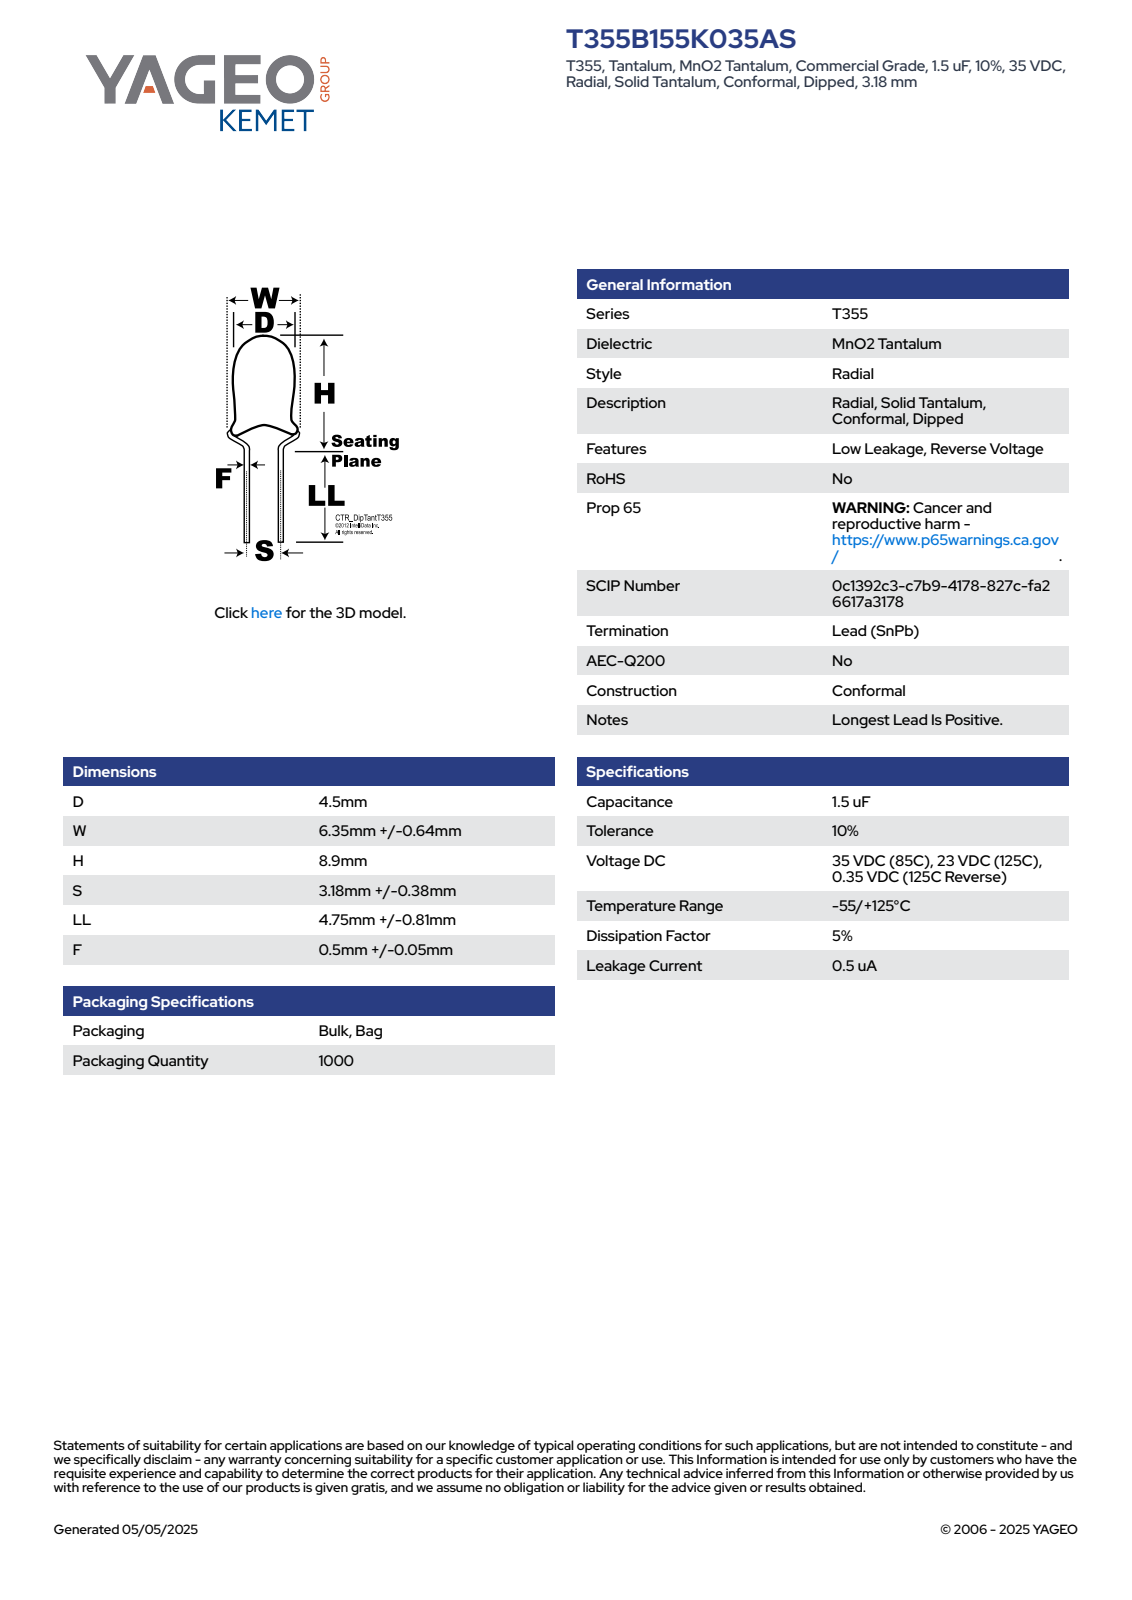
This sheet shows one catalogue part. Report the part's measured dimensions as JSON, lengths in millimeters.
{"part_name": "CTR_T355_D4.5W6.99H8.9S3.18LL5.56F0.55", "step_written_by": "SolidWorks 2021 (AUTOMOTIVE_DESIGN)", "units": "millimeters", "bodies": {"solids": 1, "faces": 100, "planar": 30, "cylindrical": 6, "other": 64}, "overall_size": [14.46, 6.99, 4.5], "volume_mm3": 89, "surface_area_mm2": 138, "round_bosses_or_shafts": [[4.5, 1]], "partial_cylinders_radius": [[2.24, 1]], "face_to_face_distances": [6.21, 8.25, 14.46, 11.73, 3.48, 2.73, 11.12, 2.87, 0.61, 3.34]}
